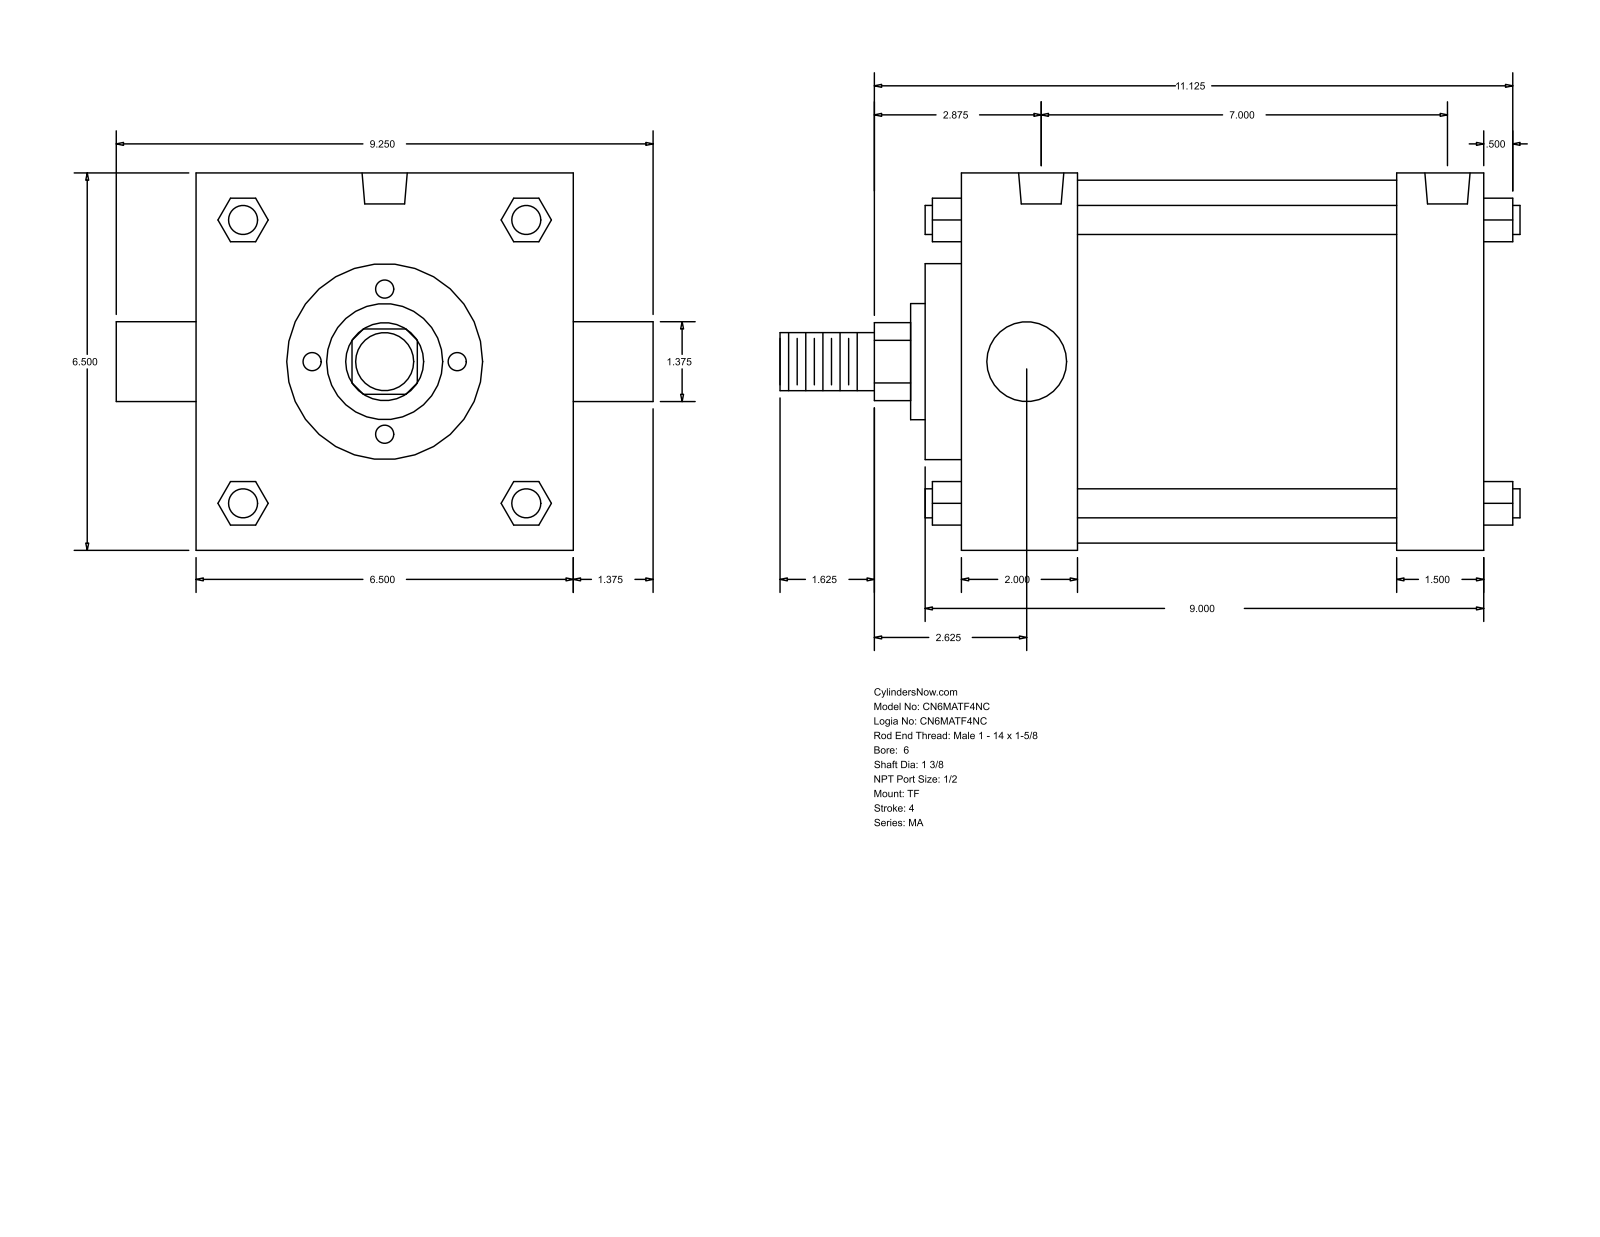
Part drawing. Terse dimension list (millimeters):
name: MA_TF__0600_1.375
written by: GSSL Pune (CONFIG_CONTROL_DESIGN)
unit: mm
bodies: 0 solids, 122 faces (93 planar, 29 cylindrical, 0 other)
size: 323.85 × 234.95 × 165.1
holes: 3× ⌀17.46, 2× ⌀19.77
bosses: 4× ⌀12.7, 2× ⌀34.92, 1× ⌀158.75, 1× ⌀85.72, 1× ⌀50.8, 1× ⌀25.4
rounds: 1× R17.06
face distances: 165.1, 231.78, 38.1, 50.8, 180.98, 193.68, 142.88, 66.67, 15.87, 209.55
hole spacings: 3.18, 177.79, 180.97
